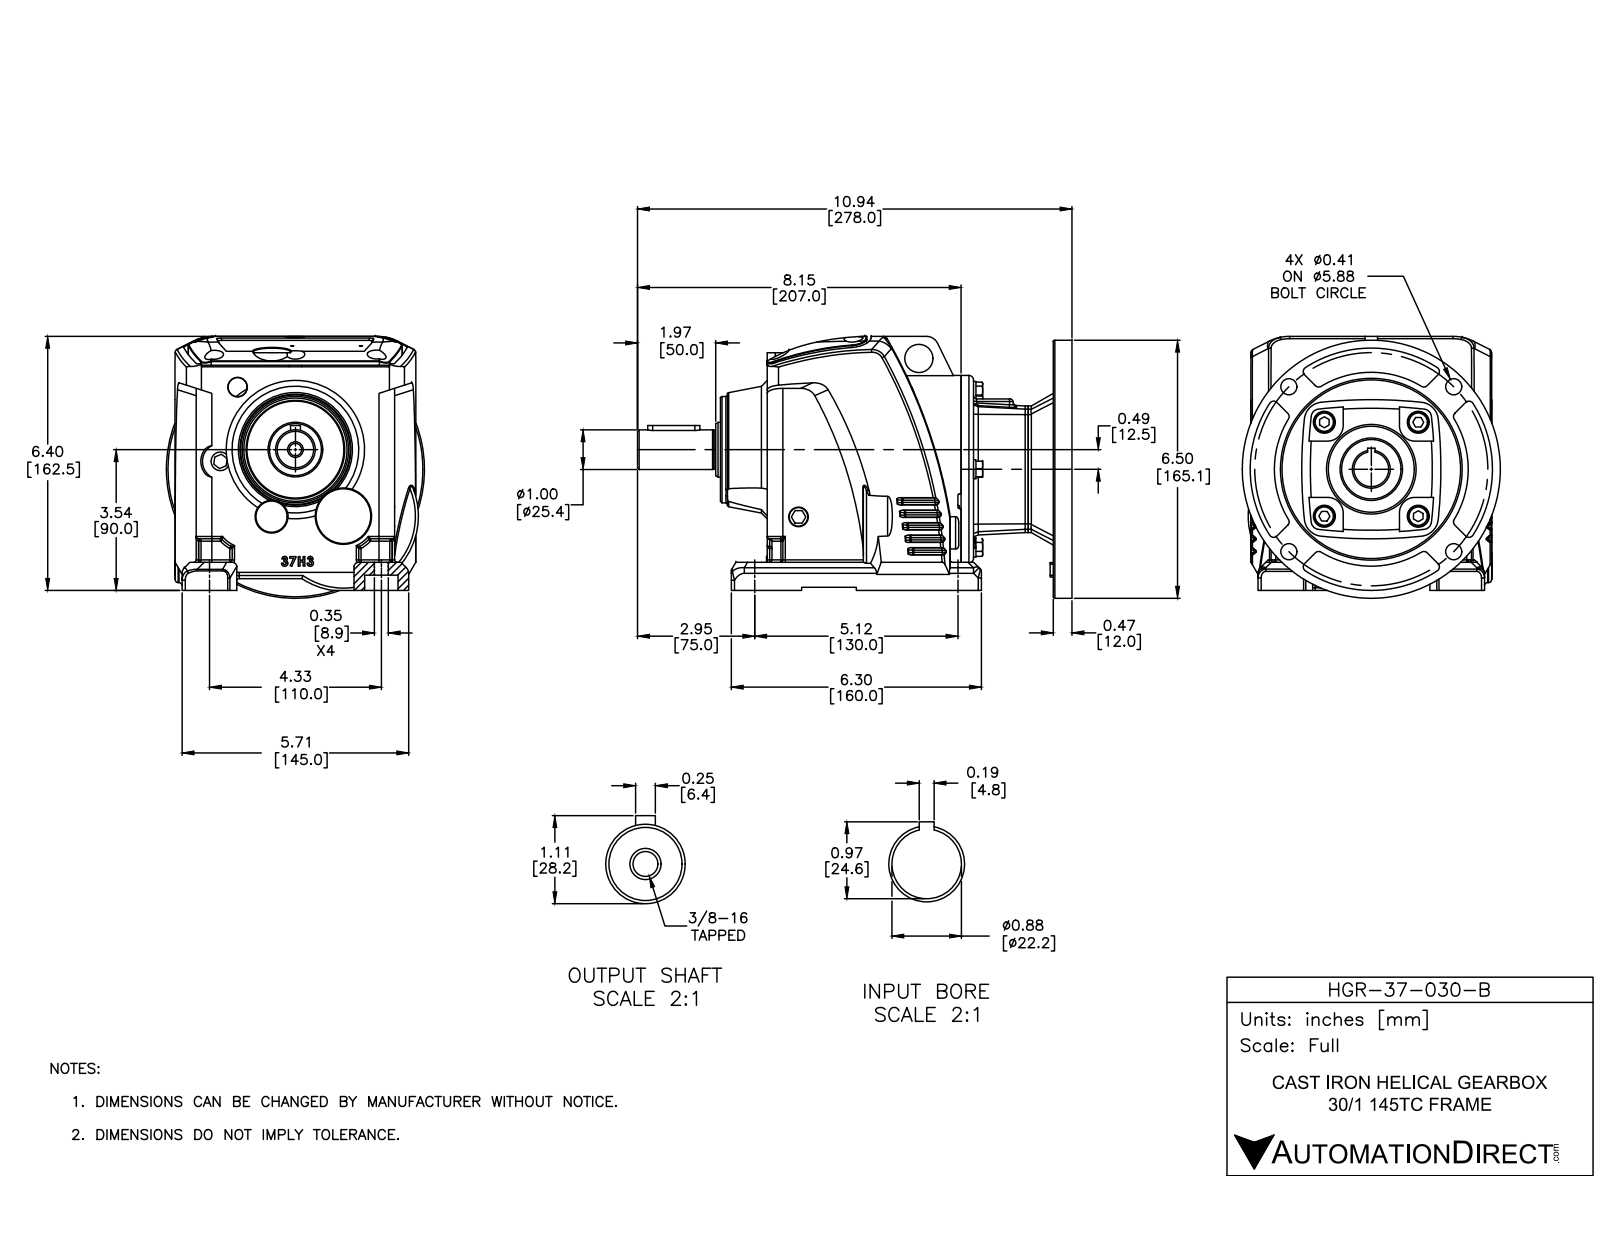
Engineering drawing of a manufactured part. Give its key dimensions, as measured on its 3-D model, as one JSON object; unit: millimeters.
{"part_name": "HGR-37-030-B", "step_written_by": "SolidWorks 2015 (CONFIG_CONTROL_DESIGN)", "units": "millimeters", "bodies": {"solids": 28, "faces": 1025, "planar": 348, "cylindrical": 289, "other": 388}, "overall_size": [278, 167.5, 165.1], "volume_mm3": 3066000, "surface_area_mm2": 308500, "round_holes": [[12, 6], [10.3, 4], [14, 4], [7, 3], [2, 2], [9, 2], [10, 2], [8, 1], [13.5, 1], [18, 1], [22.2, 1], [35, 1]], "round_bosses_or_shafts": [[13, 7], [12.2, 4], [165.1, 1], [120, 1], [68, 1], [62, 1], [55, 1], [35, 1]], "partial_cylinders_radius": [[1.5, 43], [3, 19], [2, 18], [10, 10], [5, 8], [8, 5], [4, 4], [7, 4]], "face_to_face_distances": [7, 16, 59, 28, 190, 43, 183, 8, 23, 66], "hole_center_spacings": [32.1, 42.5, 74.6, 85.9, 85.9, 117.1, 34.8, 47.4]}
